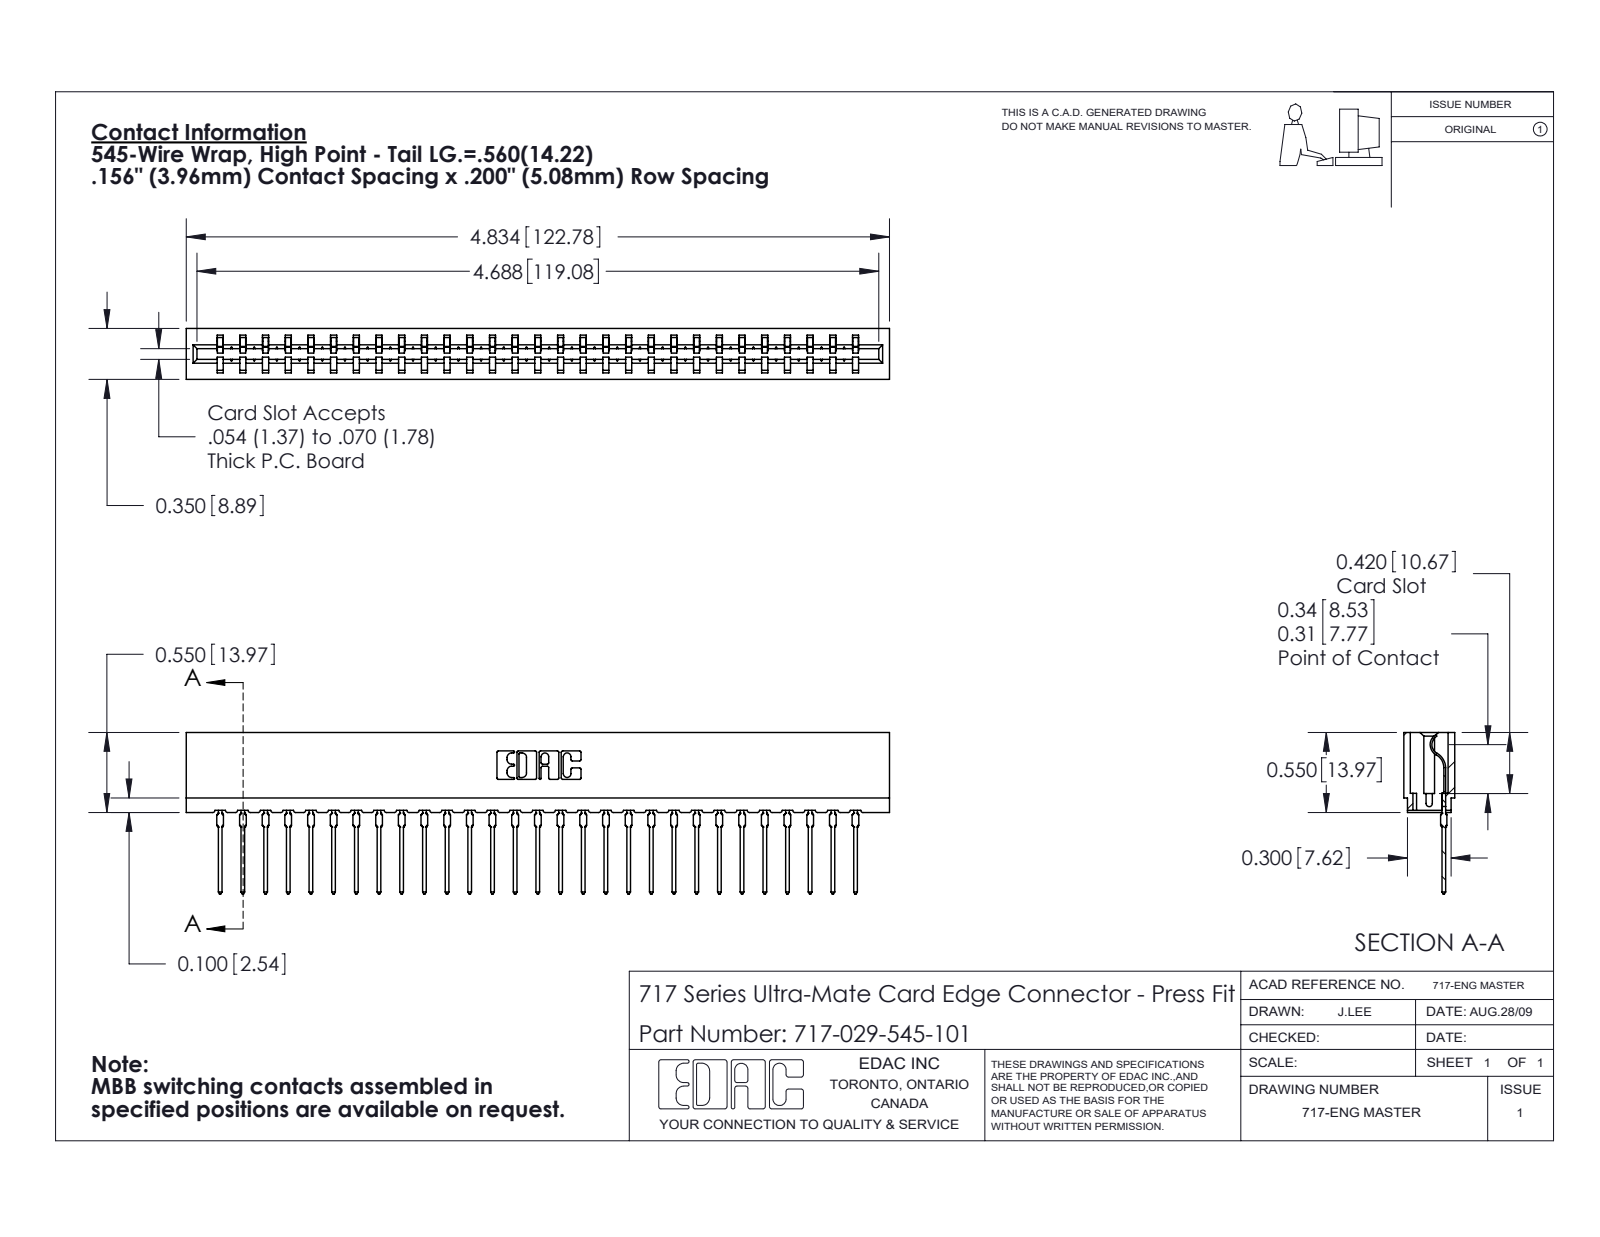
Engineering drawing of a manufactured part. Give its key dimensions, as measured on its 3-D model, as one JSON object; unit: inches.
{"part_name": "717 Part_Insulator Option - 06; 717-029-545-101; 745-292-001_545", "step_written_by": "SolidWorks 2020 (CONFIG_CONTROL_DESIGN)", "units": "inches", "bodies": {"solids": 30, "faces": 3371, "planar": 2026, "cylindrical": 591, "other": 754}, "overall_size": [4.834, 1.109, 0.35], "volume_in3": 0.641, "surface_area_in2": 23.37, "partial_cylinders_radius": [[0.015, 58], [0.021, 58], [0.01, 22], [0.007, 6], [0.031, 6], [0.005, 4], [0.011, 4], [0.026, 3]], "face_to_face_distances": [0.212, 0.138, 0.35, 0.074, 0.063, 0.287, 0.076, 0.149, 0.156, 0.045]}
